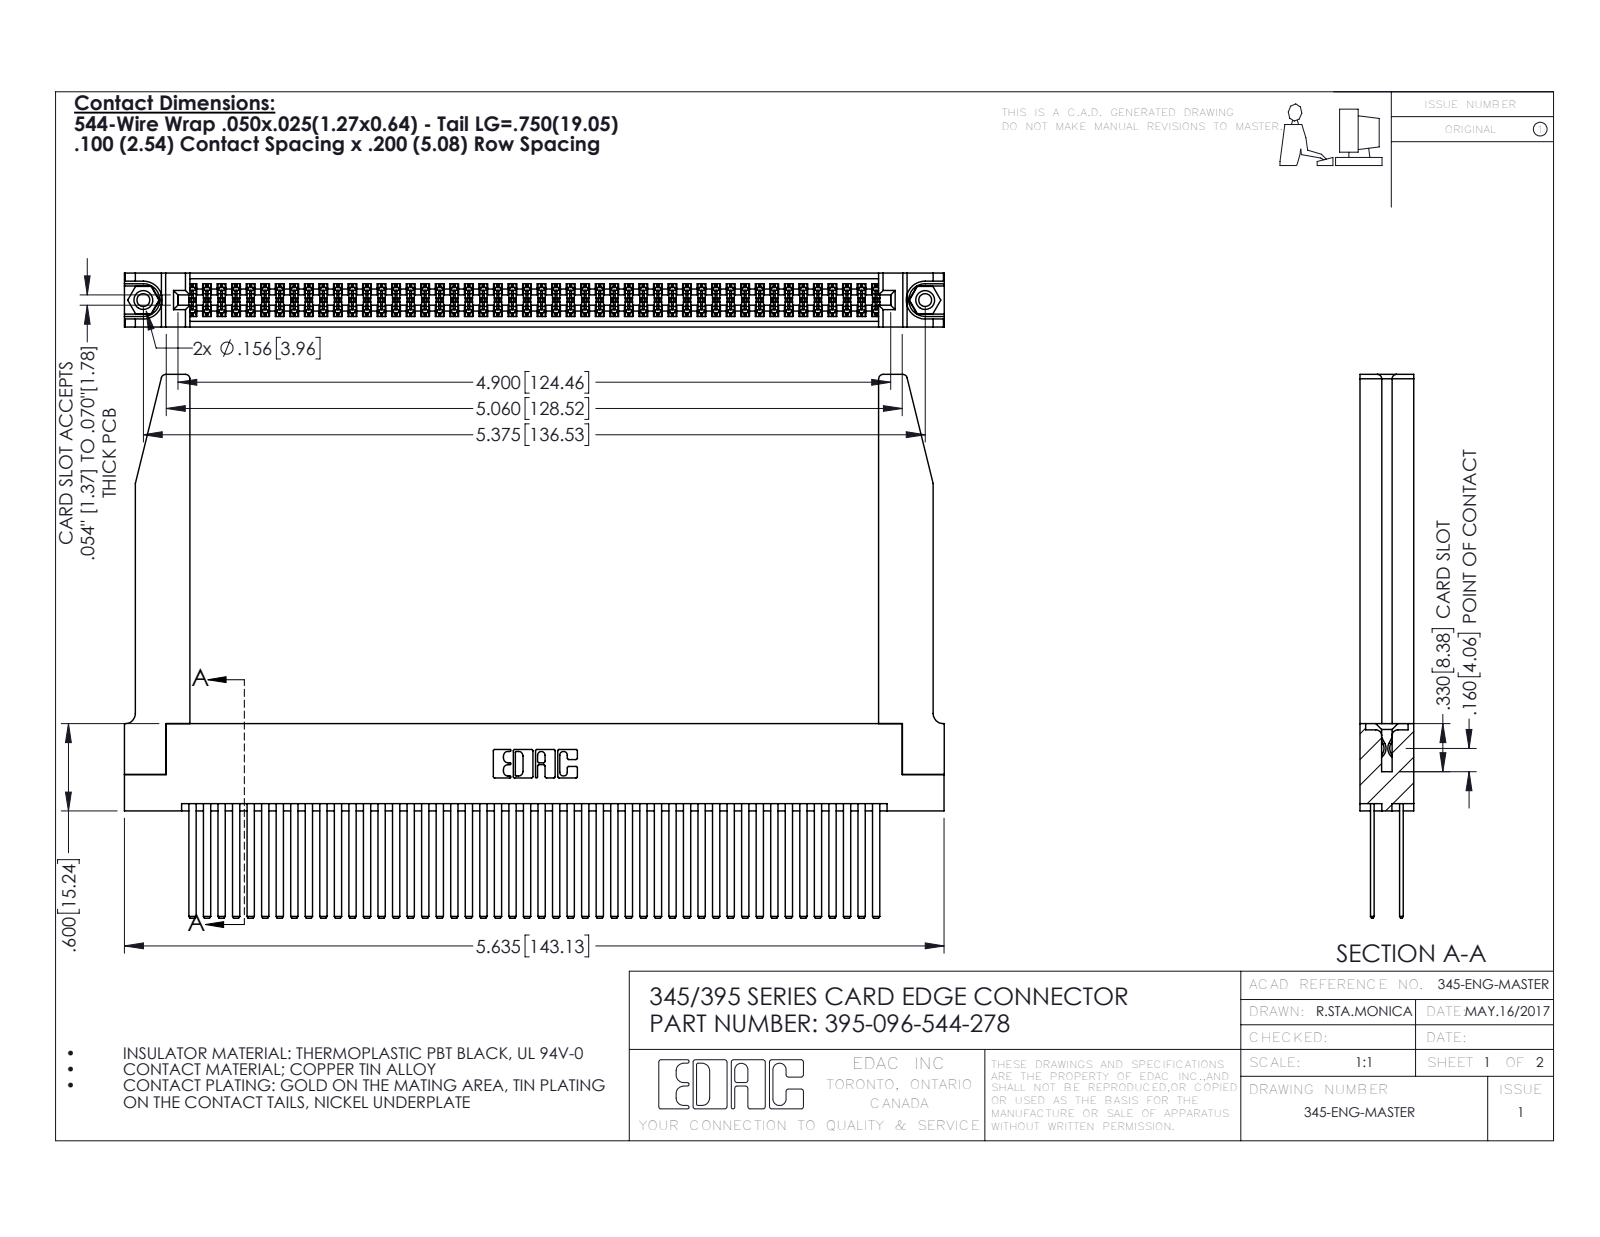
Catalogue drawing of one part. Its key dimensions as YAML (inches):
part_name: "345-220-078_345-220-078; 395-096-544-278; 345 Part_Flush Mounting Lugs - 0.156 Dia-TH; 345-292-001_345-293-144 (+1 more)"
step_written_by: "SolidWorks 2016 (CONFIG_CONTROL_DESIGN)"
units: inches
bodies: {solids: 101, faces: 4584, planar: 3006, cylindrical: 1526, other: 52}
overall_size: [5.636, 3.737, 0.37]
volume: 1.408
surface_area: 51.97
round_holes:
  - {diameter: 0.089, count: 2}
  - {diameter: 0.125, count: 2}
  - {diameter: 0.156, count: 2}
  - {diameter: 0.064, count: 1}
round_bosses_or_shafts:
  - {diameter: 0.155, count: 2}
partial_cylinders:
  - {radius: 0.006, count: 144}
  - {radius: 0.01, count: 22}
  - {radius: 0.03, count: 8}
  - {radius: 0.007, count: 6}
  - {radius: 0.031, count: 6}
  - {radius: 0.026, count: 3}
  - {radius: 0.014, count: 2}
  - {radius: 0.019, count: 2}
face_to_face_distances: [0.072, 0.298, 0.2, 0.098, 0.272, 0.025, 0.37, 0.225, 0.175, 0.15]
hole_center_spacings: [0.27, 5.139, 5.375]
